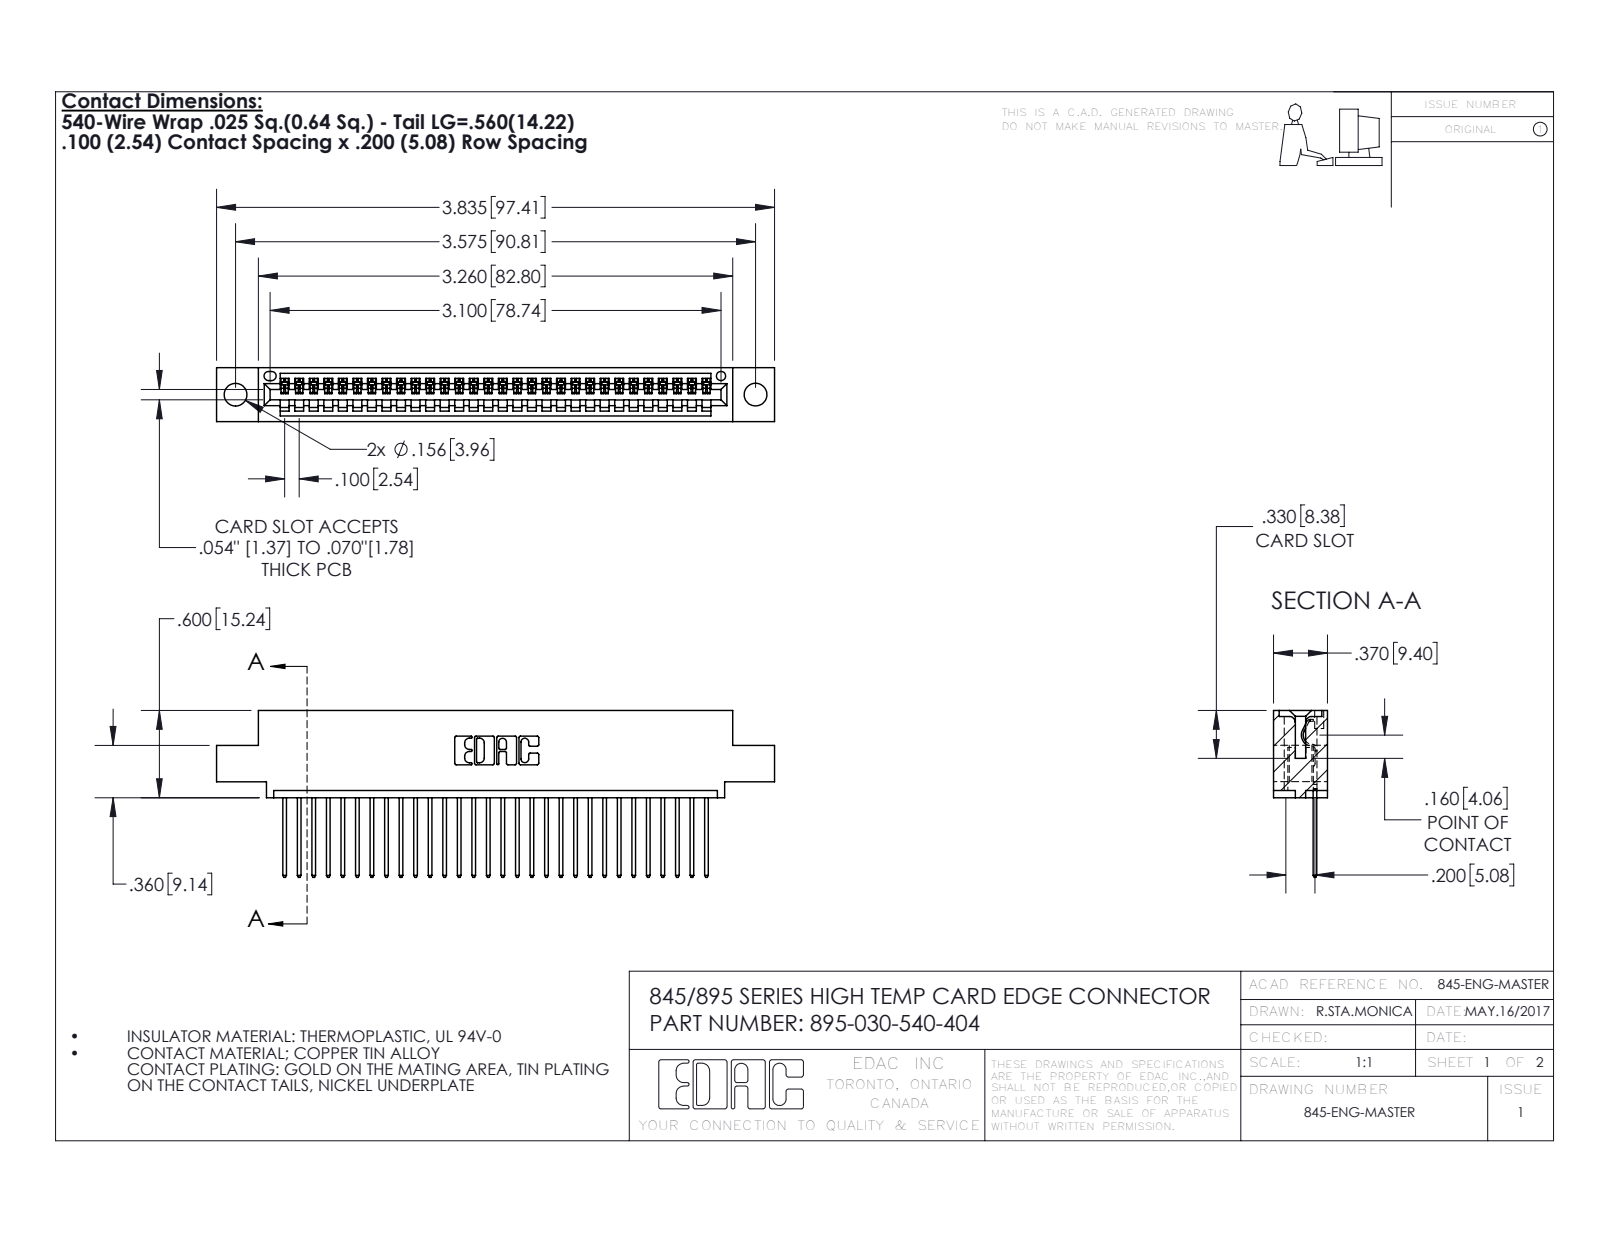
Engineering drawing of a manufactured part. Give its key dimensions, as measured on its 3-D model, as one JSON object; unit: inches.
{"part_name": "395-030-540-404; 345-292-001_345-293-140; 345 Part_0.110 Offset - 0.156 Dia-TH", "step_written_by": "SolidWorks 2016 (CONFIG_CONTROL_DESIGN)", "units": "inches", "bodies": {"solids": 31, "faces": 1870, "planar": 1284, "cylindrical": 586, "other": 0}, "overall_size": [3.835, 1.147, 0.37], "volume_in3": 0.551, "surface_area_in2": 18.64, "round_holes": [[0.156, 2], [0.064, 1]], "partial_cylinders_radius": [[0.006, 60], [0.01, 60], [0.01, 22], [0.007, 6], [0.031, 6], [0.026, 3], [0.031, 2], [0.04, 2]], "face_to_face_distances": [0.298, 0.072, 0.37, 0.2, 0.098, 0.272, 0.025, 0.225, 0.149, 0.072], "hole_center_spacings": [0.27, 3.34, 3.575]}
